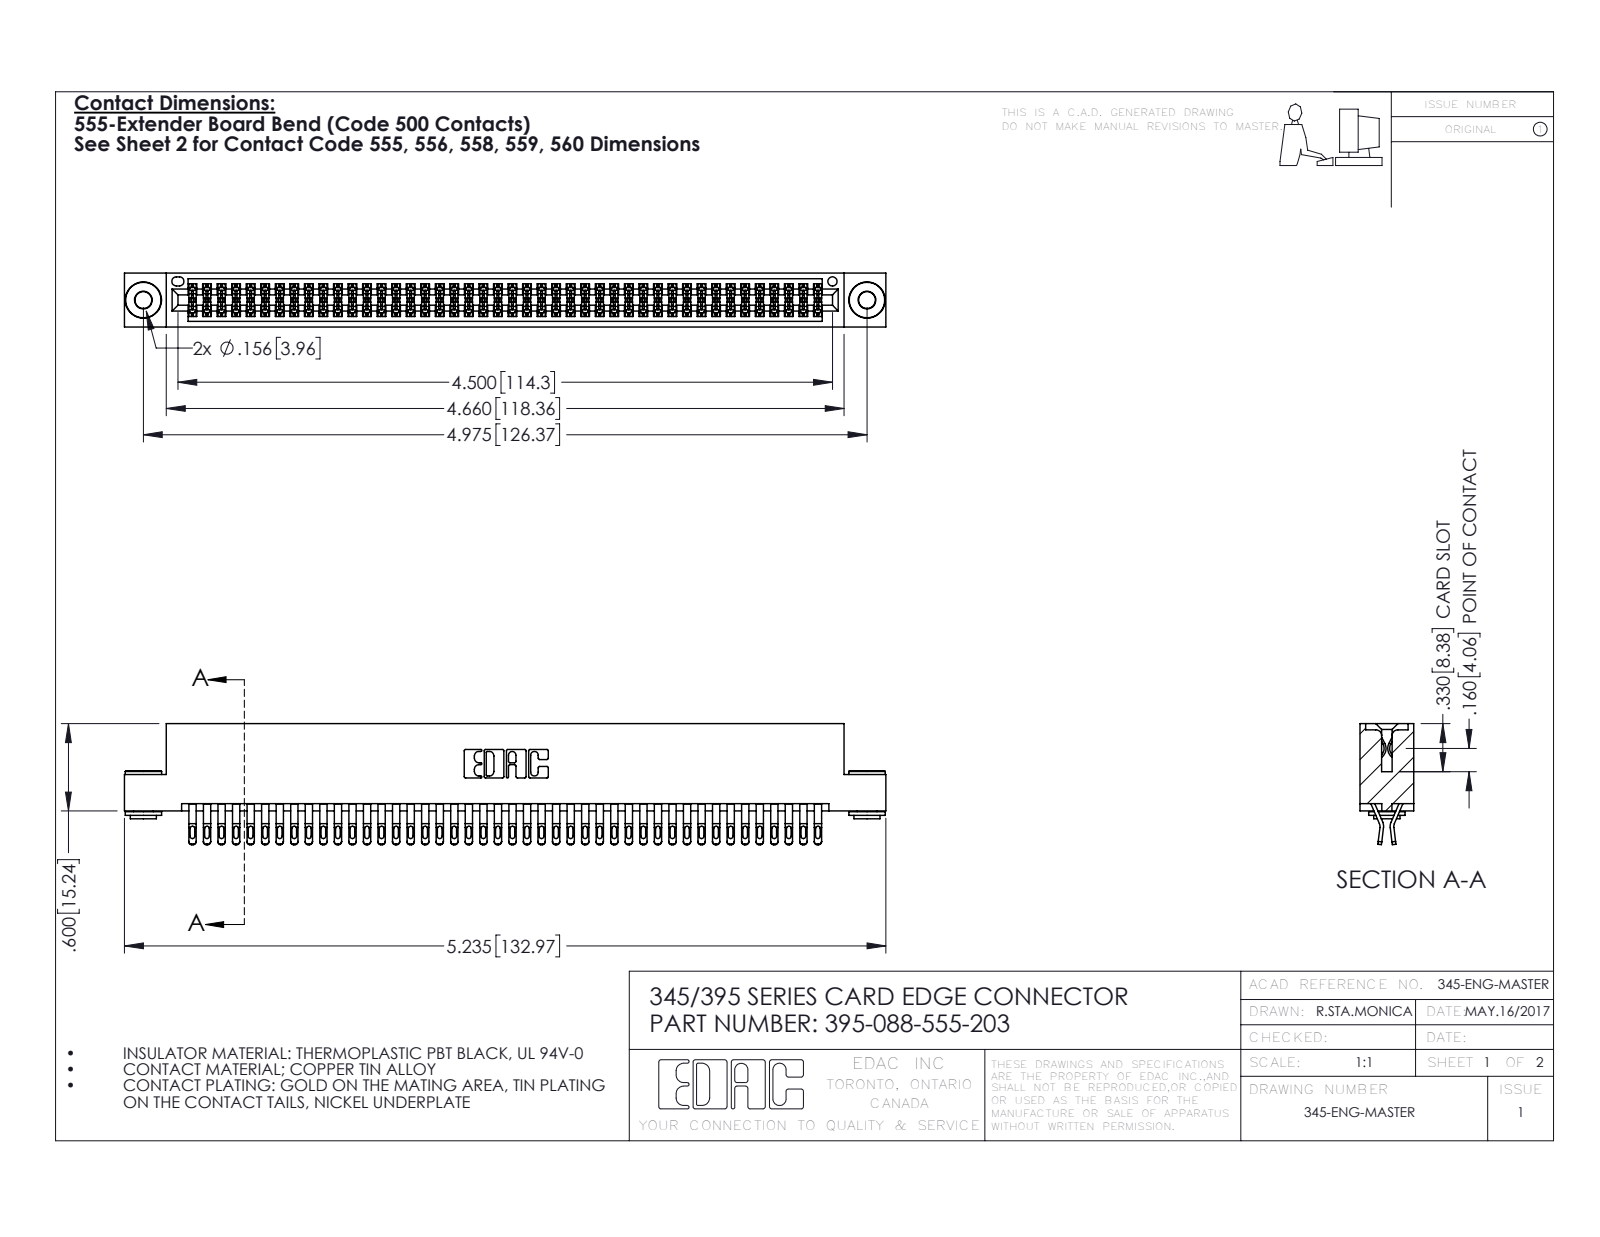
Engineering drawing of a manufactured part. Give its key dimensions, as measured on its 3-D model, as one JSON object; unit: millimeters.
{"part_name": "345-250-002_345-250-002-102; 345-292-001_555 Tail; 345 Part_Flush Mounting Lugs - 0.156 Dia-TH; 395-088-555-203", "step_written_by": "SolidWorks 2016 (CONFIG_CONTROL_DESIGN)", "units": "millimeters", "bodies": {"solids": 91, "faces": 5092, "planar": 2818, "cylindrical": 2266, "other": 8}, "overall_size": [133, 21.1, 9.4], "volume_mm3": 13200, "surface_area_mm2": 20660, "round_holes": [[2.9, 2], [4, 2], [1.6, 1]], "round_bosses_or_shafts": [[6.4, 2], [4.6, 2], [3.5, 2]], "partial_cylinders_radius": [[0.4, 220], [0.5, 176], [0.2, 132], [0.3, 22], [0.2, 6], [0.8, 6], [0.7, 3], [0.3, 2]], "face_to_face_distances": [1.8, 7.6, 0.6, 5.1, 9.4, 2.5, 6.9, 5.7, 4.4, 3.8], "hole_center_spacings": [6.9, 120.4, 126.4]}
